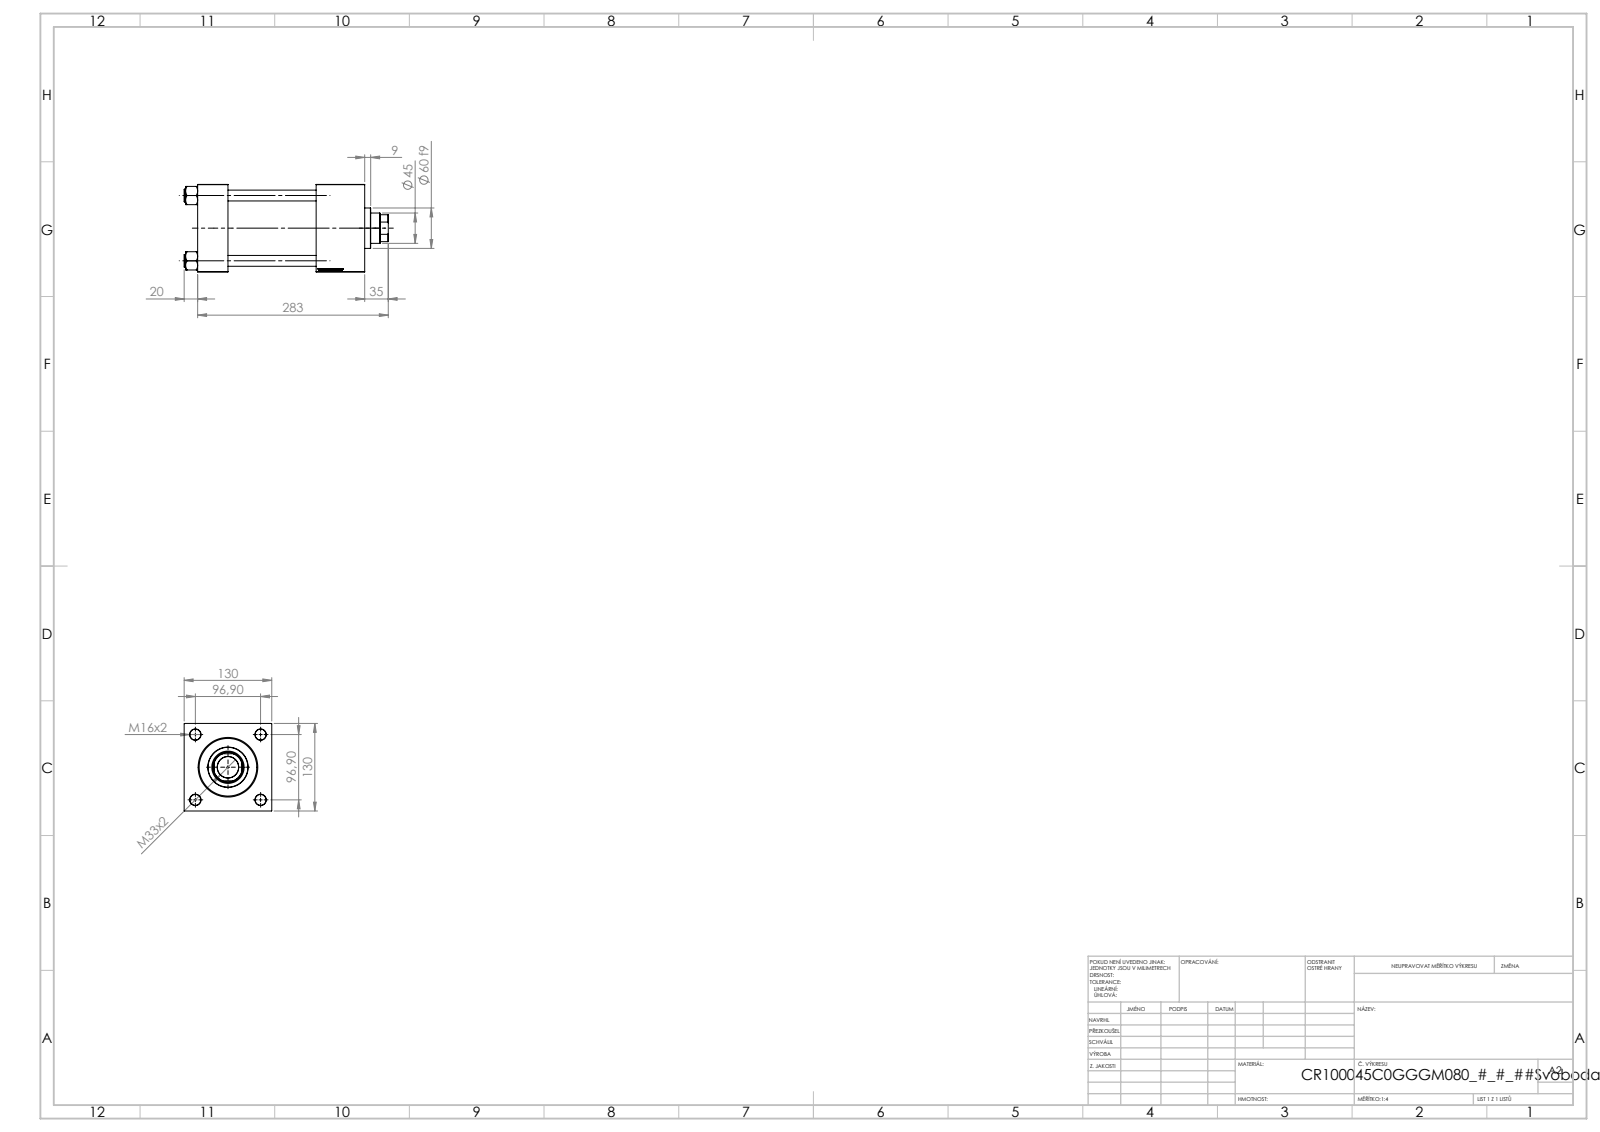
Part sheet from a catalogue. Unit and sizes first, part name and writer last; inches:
Units: inches
Overall size (bounding box): 11.929 × 5.118 × 5.118
Round holes (diameter × count): ⌀0.63 ×4, ⌀0.276 ×2, ⌀1.041 ×2, ⌀1.378 ×2, ⌀1.24 ×1, ⌀1.772 ×1, ⌀1.89 ×1, ⌀2.992 ×1, ⌀3.366 ×1, ⌀3.937 ×1
Round bosses / shafts (diameter × count): ⌀0.748 ×4, ⌀4.173 ×1, ⌀2.362 ×1
Partial cylindrical surfaces — rounded edges, fillets, slot ends (radius × count): R0.866 ×1
Main face-to-face distances: 5.118, 1.772, 9.764, 7.992, 6.929, 5.157, 2.835, 3.15, 3.78, 2.008
Hole centre spacings: 2.698, 3.815, 5.395, 7.028
Volume: 160.3 in³ · Surface area: 597.9 in²
Bodies: 11 solids, 1197 faces (574 planar, 87 cylindrical, 536 other)
Part name (STEP PRODUCT): V215CR_C_TYCINKA; V215CR_C_Body; V215_VC_A; V215CR_VCP_C (+1 more)
STEP written by: SolidWorks 2019 (CONFIG_CONTROL_DESIGN)
